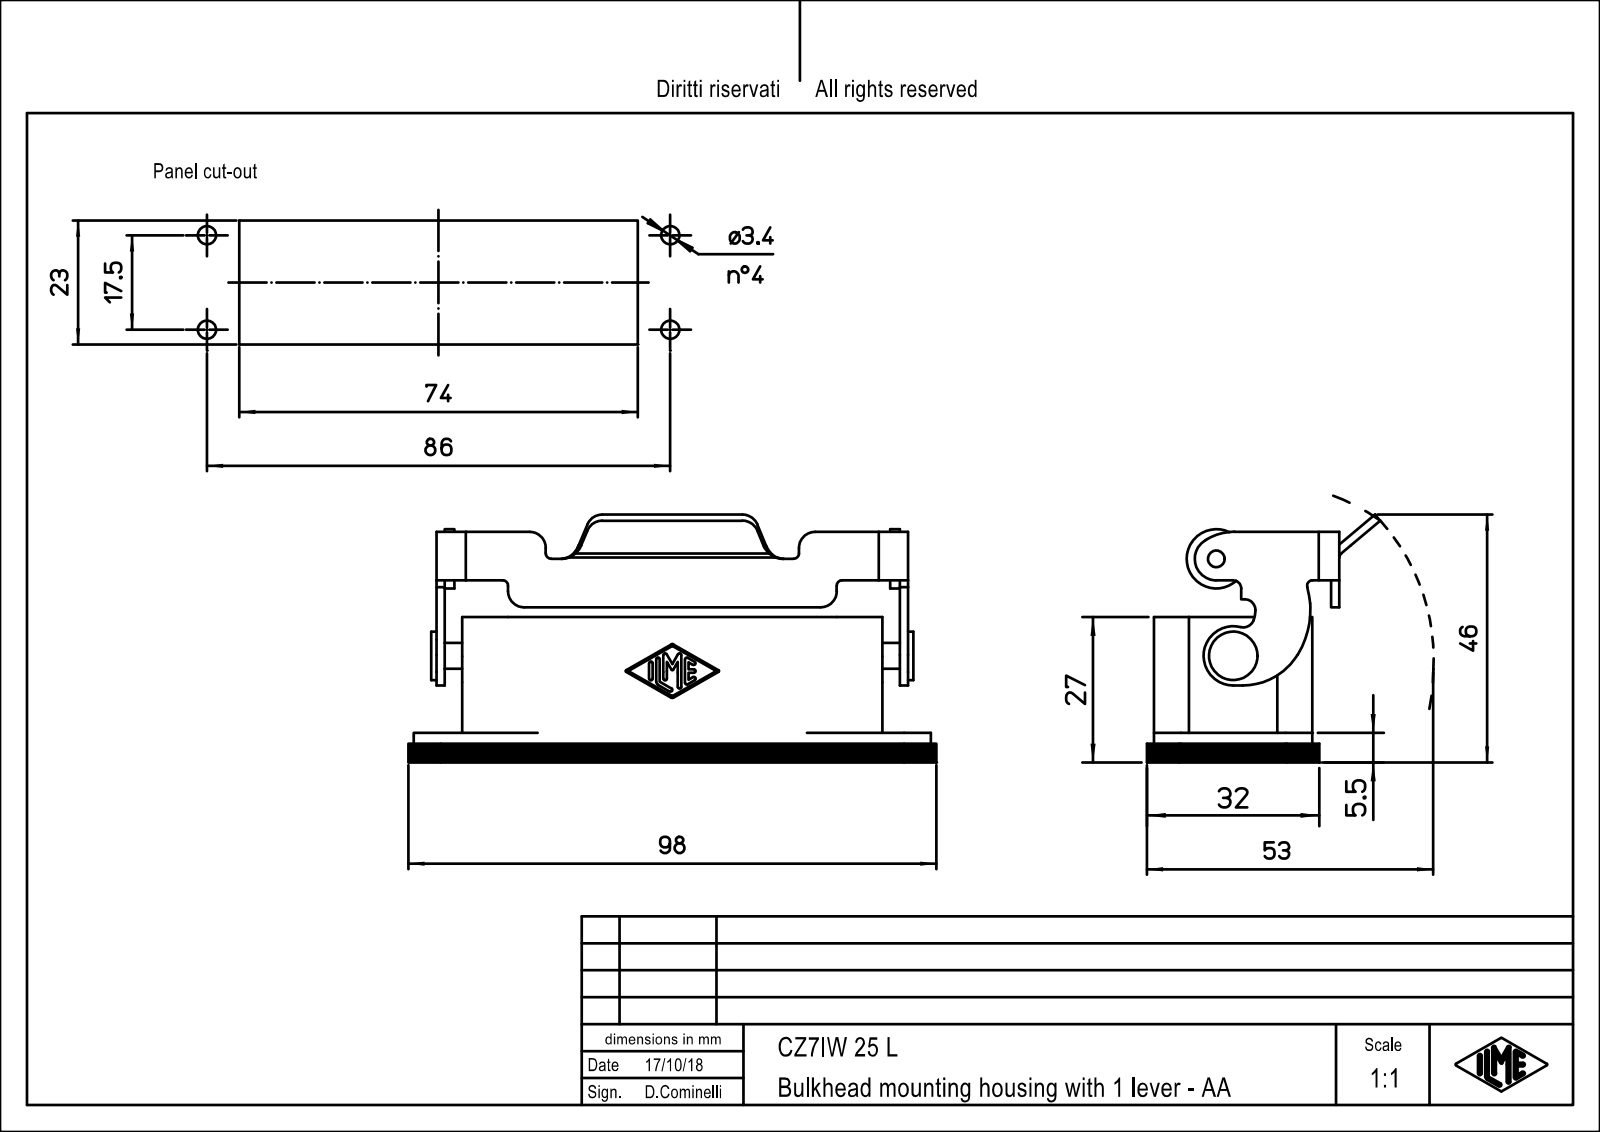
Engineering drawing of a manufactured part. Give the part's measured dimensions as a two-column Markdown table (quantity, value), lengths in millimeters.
| quantity | value |
| --- | --- |
| part name | CZ7IW_25_L |
| STEP written by | PTC Creo Elements/Direct Modeling 19.0E 27-Jun-2016 (C) Parametric Technology GmbH (AUTOMOTIVE_DESIGN) |
| units | millimeters |
| bodies | 1 solid, 196 faces (90 planar, 106 cylindrical, 0 other) |
| overall size | 98 × 46.2 × 43.28 |
| volume | 24 365 mm³ |
| surface area | 20 138 mm² |
| round holes (diameter × count) | 3 × 4, 3.4 × 4, 3.1 × 1, 5 × 1 |
| round bosses / shafts (diameter × count) | 4.8 × 2, 11 × 1, 9 × 1, 7 × 1 |
| partial cylindrical surfaces (radius × count) | 3 × 12, 1 × 6, 3.5 × 6, 2.5 × 5, 5 × 4, 6 × 4, 6.5 × 4, 2 × 2 |
| main face-to-face distances | 1.5, 29.4, 3.5, 5, 87, 34.4, 32.9, 84, 5.5, 4.5 |
| hole center spacings | 10.03, 19.51, 76, 77.82, 16, 17.5, 66, 67.91 |
